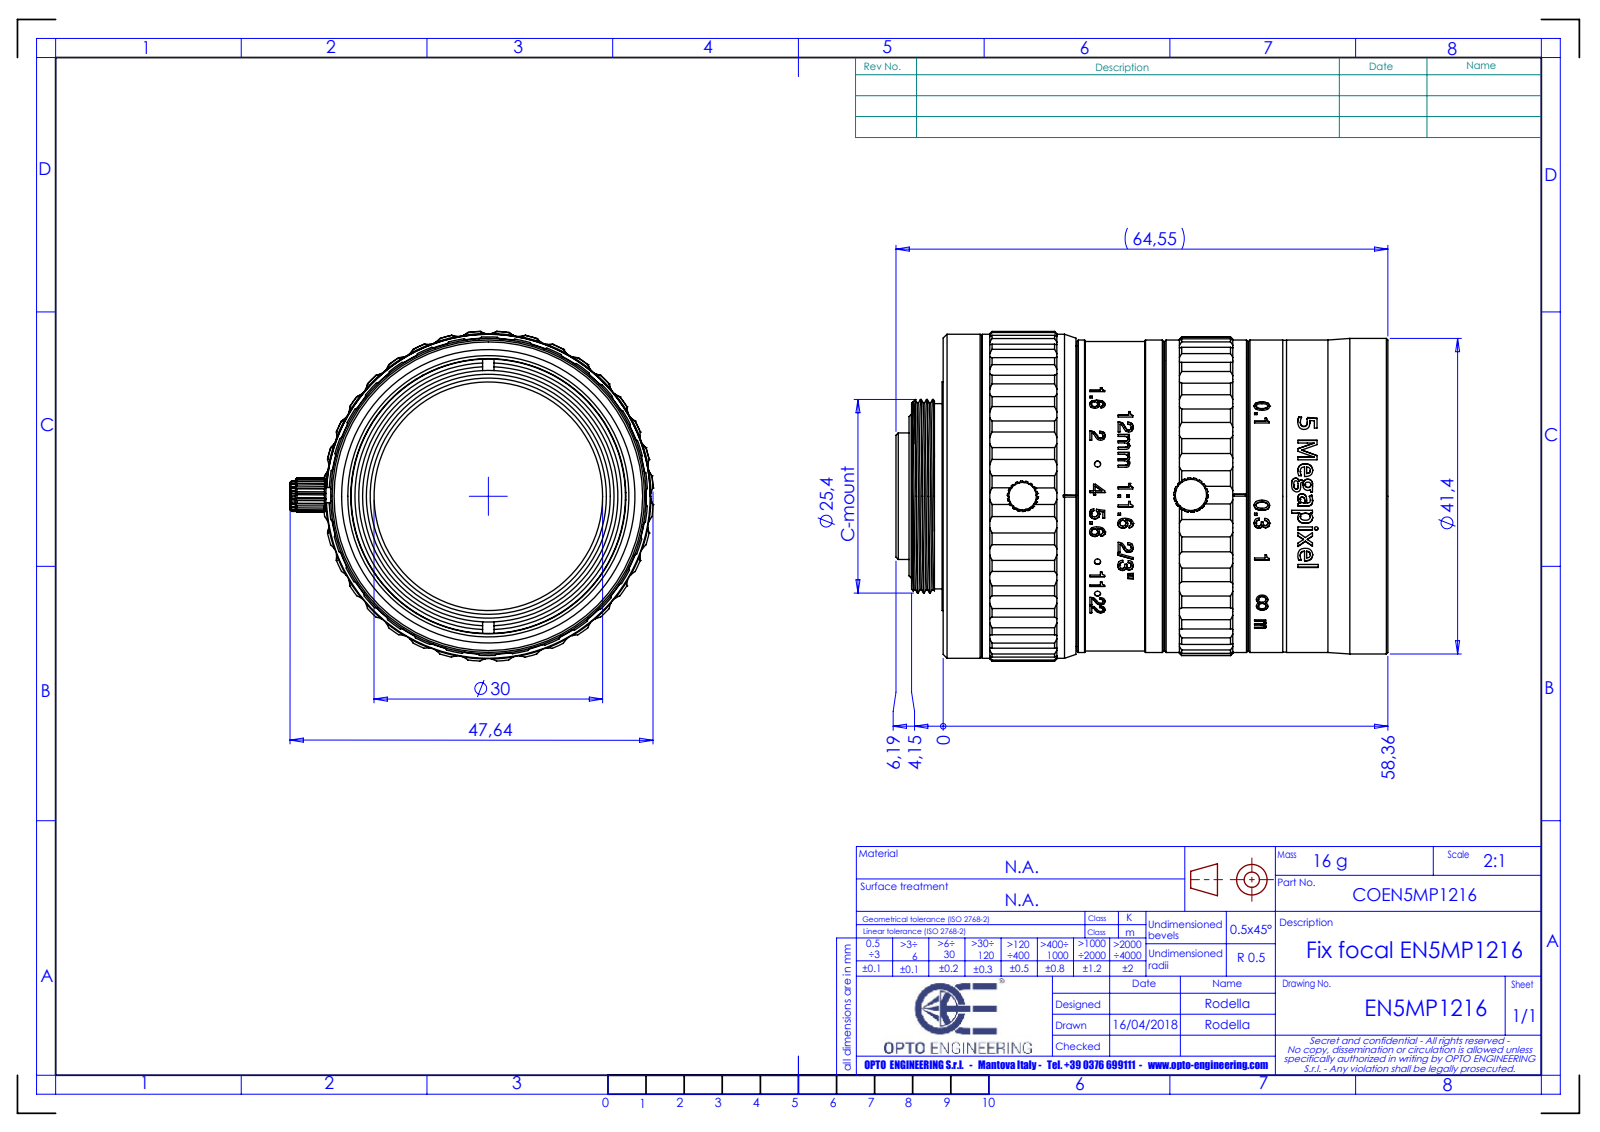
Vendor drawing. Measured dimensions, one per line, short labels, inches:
name: PRT0046_AF0; PRT0047_AF0; PRT0050_AF0; PRT0050 (+8 more)
written by: PRO/ENGINEER BY PARAMETRIC TECHNOLOGY CORPORATION, 2011310 (AUTOMOTIVE_DESIGN)
unit: in
bodies: 15 solids, 1623 faces (601 planar, 396 cylindrical, 626 other)
size: 2.541 × 1.876 × 1.703
volume: 0.984 in³; area: 39.6 in²
holes: 4× ⌀0.059, 3× ⌀0.102, 1× ⌀0.063, 1× ⌀0.512, 1× ⌀0.567, 1× ⌀0.709, 1× ⌀0.748, 1× ⌀0.846, 1× ⌀1.079, 1× ⌀1.181, 1× ⌀1.189, 1× ⌀1.22
bosses: 3× ⌀0.098, 3× ⌀0.055, 2× ⌀0.079, 1× ⌀1.673, 1× ⌀1.63, 1× ⌀1.614, 1× ⌀1.61, 1× ⌀1.606
rounds: 67× R0.079, 4× R0.039, 3× R0.018, 1× R0.089, 1× R0.798, 1× R0.802, 1× R0.807, 1× R0.813
face distances: 0.043, 2.052, 2.095, 0.039, 1.542, 0.159, 2.264, 0.018, 2.07, 2.113
hole spacings: 0.689, 1.193, 1.194
